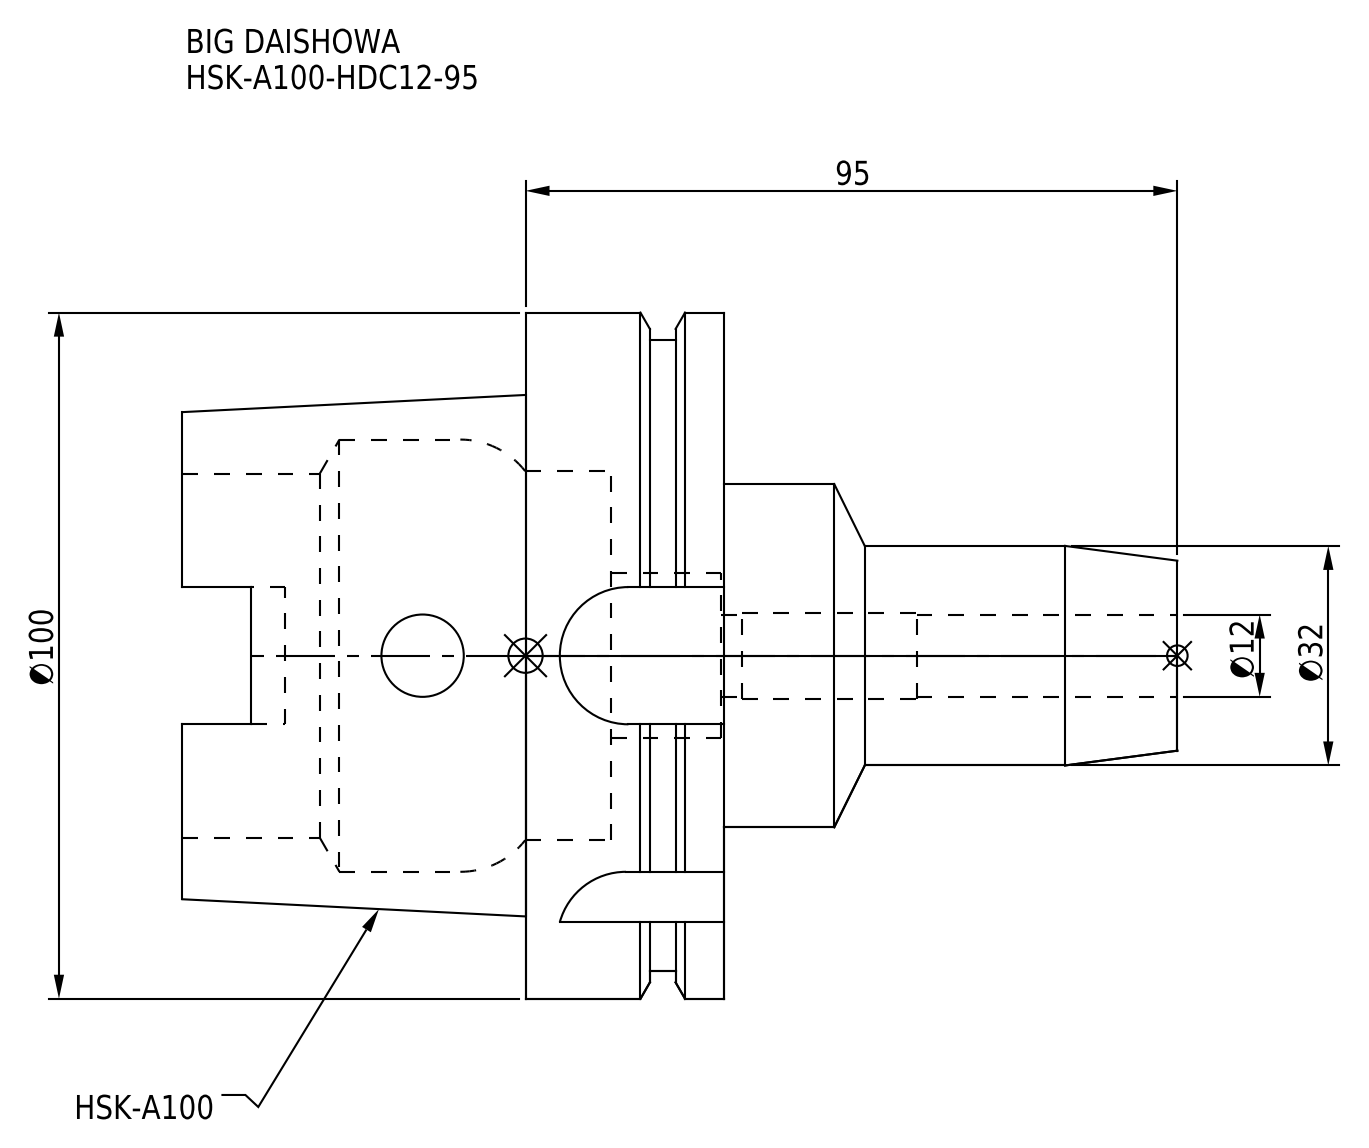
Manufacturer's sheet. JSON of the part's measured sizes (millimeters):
{"part_name": "HSK-A100-HDC12-95", "step_written_by": "CREO PARAMETRIC BY PTC INC, 2016380 (AUTOMOTIVE_DESIGN)", "units": "millimeters", "bodies": {"solids": 1, "faces": 92, "planar": 34, "cylindrical": 40, "other": 18}, "overall_size": [145, 100, 100], "volume_mm3": 318044, "surface_area_mm2": 59263, "round_holes": [[12, 2], [12.5, 1], [24, 1], [53, 1], [53.8, 1], [63, 1]], "round_bosses_or_shafts": [[100, 1], [92, 1], [50, 1], [32, 1]], "partial_cylinders_radius": [[4.88, 4], [10, 4]], "face_to_face_distances": [29, 16.55, 12.45, 79, 62.45, 50, 66, 82.55, 95, 145]}
